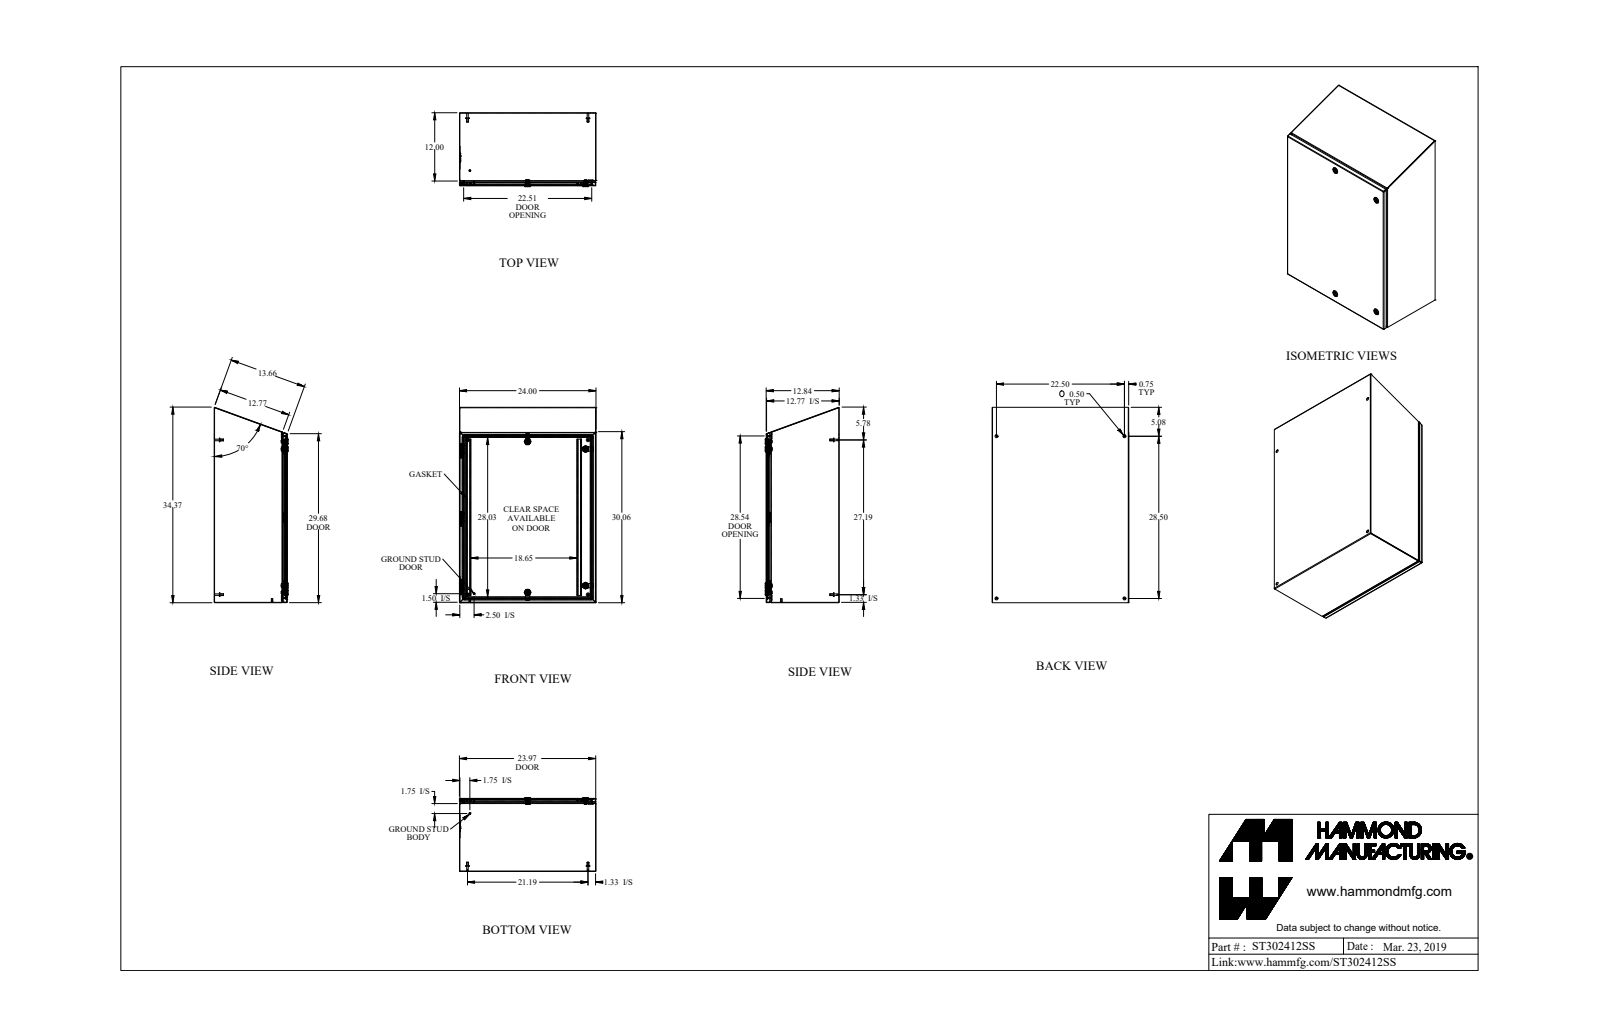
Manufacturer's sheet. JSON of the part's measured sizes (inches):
{"part_name": "ST302412SS", "step_written_by": "SolidWorks 2018 (AUTOMOTIVE_DESIGN)", "units": "inches", "bodies": {"solids": 45, "faces": 1116, "planar": 600, "cylindrical": 348, "other": 168}, "overall_size": [34.328, 24.008, 12.997], "volume_in3": 239.7, "surface_area_in2": 6717, "round_holes": [[0.5, 8], [0.197, 4], [0.387, 4], [0.63, 4], [0.768, 4], [0.172, 1], [0.24, 1], [0.242, 1]], "round_bosses_or_shafts": [[0.625, 8], [0.313, 6], [1.1, 4], [0.525, 4], [0.275, 4], [0.236, 4], [0.785, 2], [0.785, 2]], "partial_cylinders_radius": [[0.036, 18], [0.108, 18], [0.01, 12], [0.048, 12], [0.125, 8], [0.006, 6], [0.062, 6], [0.188, 6]], "face_to_face_distances": [0.072, 12.765, 12.693, 23.928, 12.837, 23.856, 24, 0.072, 11.928, 0.837], "hole_center_spacings": [22.5, 28.5, 36.311, 2.497, 2.498, 10.258, 10.271, 11.267]}
